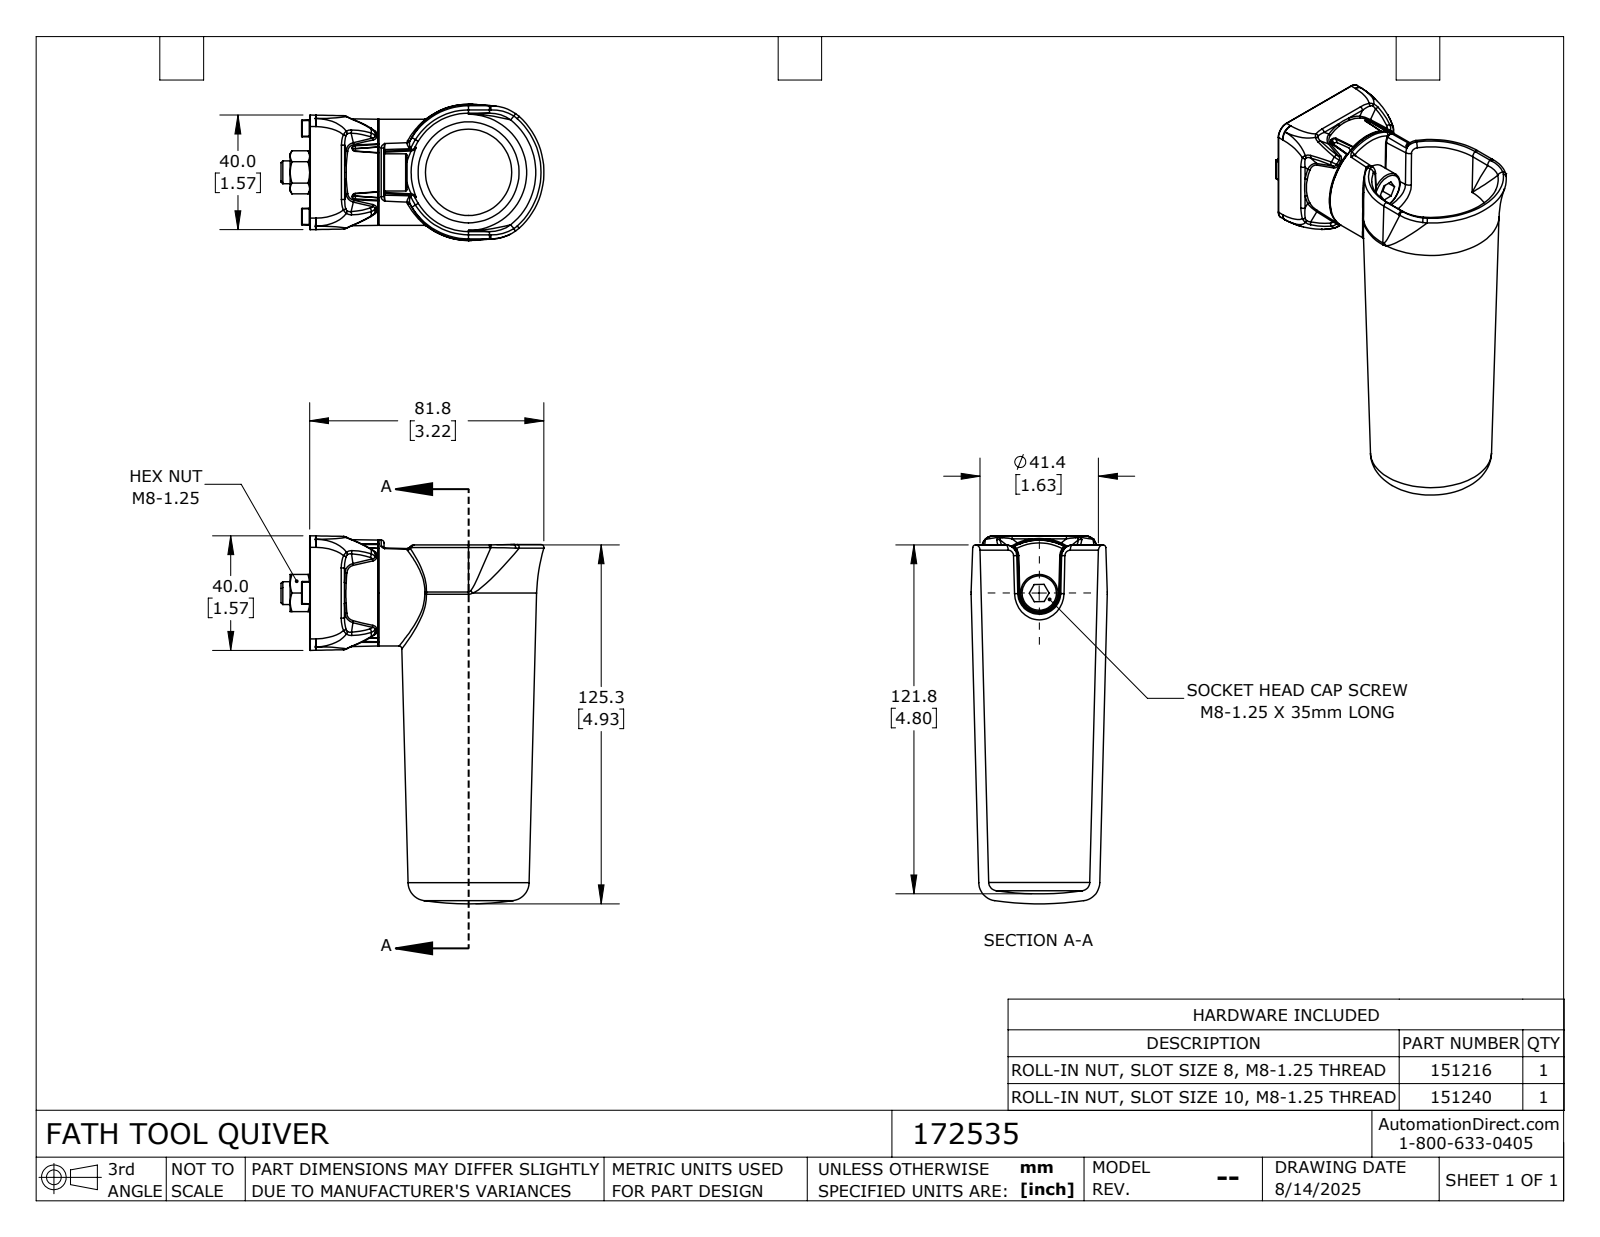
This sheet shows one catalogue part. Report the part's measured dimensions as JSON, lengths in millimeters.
{"part_name": "172535", "step_written_by": "SolidWorks 2024 (CONFIG_CONTROL_DESIGN)", "units": "millimeters", "bodies": {"solids": 6, "faces": 995, "planar": 182, "cylindrical": 259, "other": 554}, "overall_size": [128.5, 91.83, 47.56], "volume_mm3": 95920, "surface_area_mm2": 51130, "round_holes": [[6.8, 1], [8, 1], [13.01, 1]], "round_bosses_or_shafts": [[37, 1], [31, 1], [13, 1]], "partial_cylinders_radius": [[0.2, 144], [0.5, 14], [1, 10], [4, 10], [1.2, 4], [2, 2], [16.5, 1]], "face_to_face_distances": [13.5, 13.59, 30.8, 8, 6, 10.5, 24, 10.41, 17, 18]}
